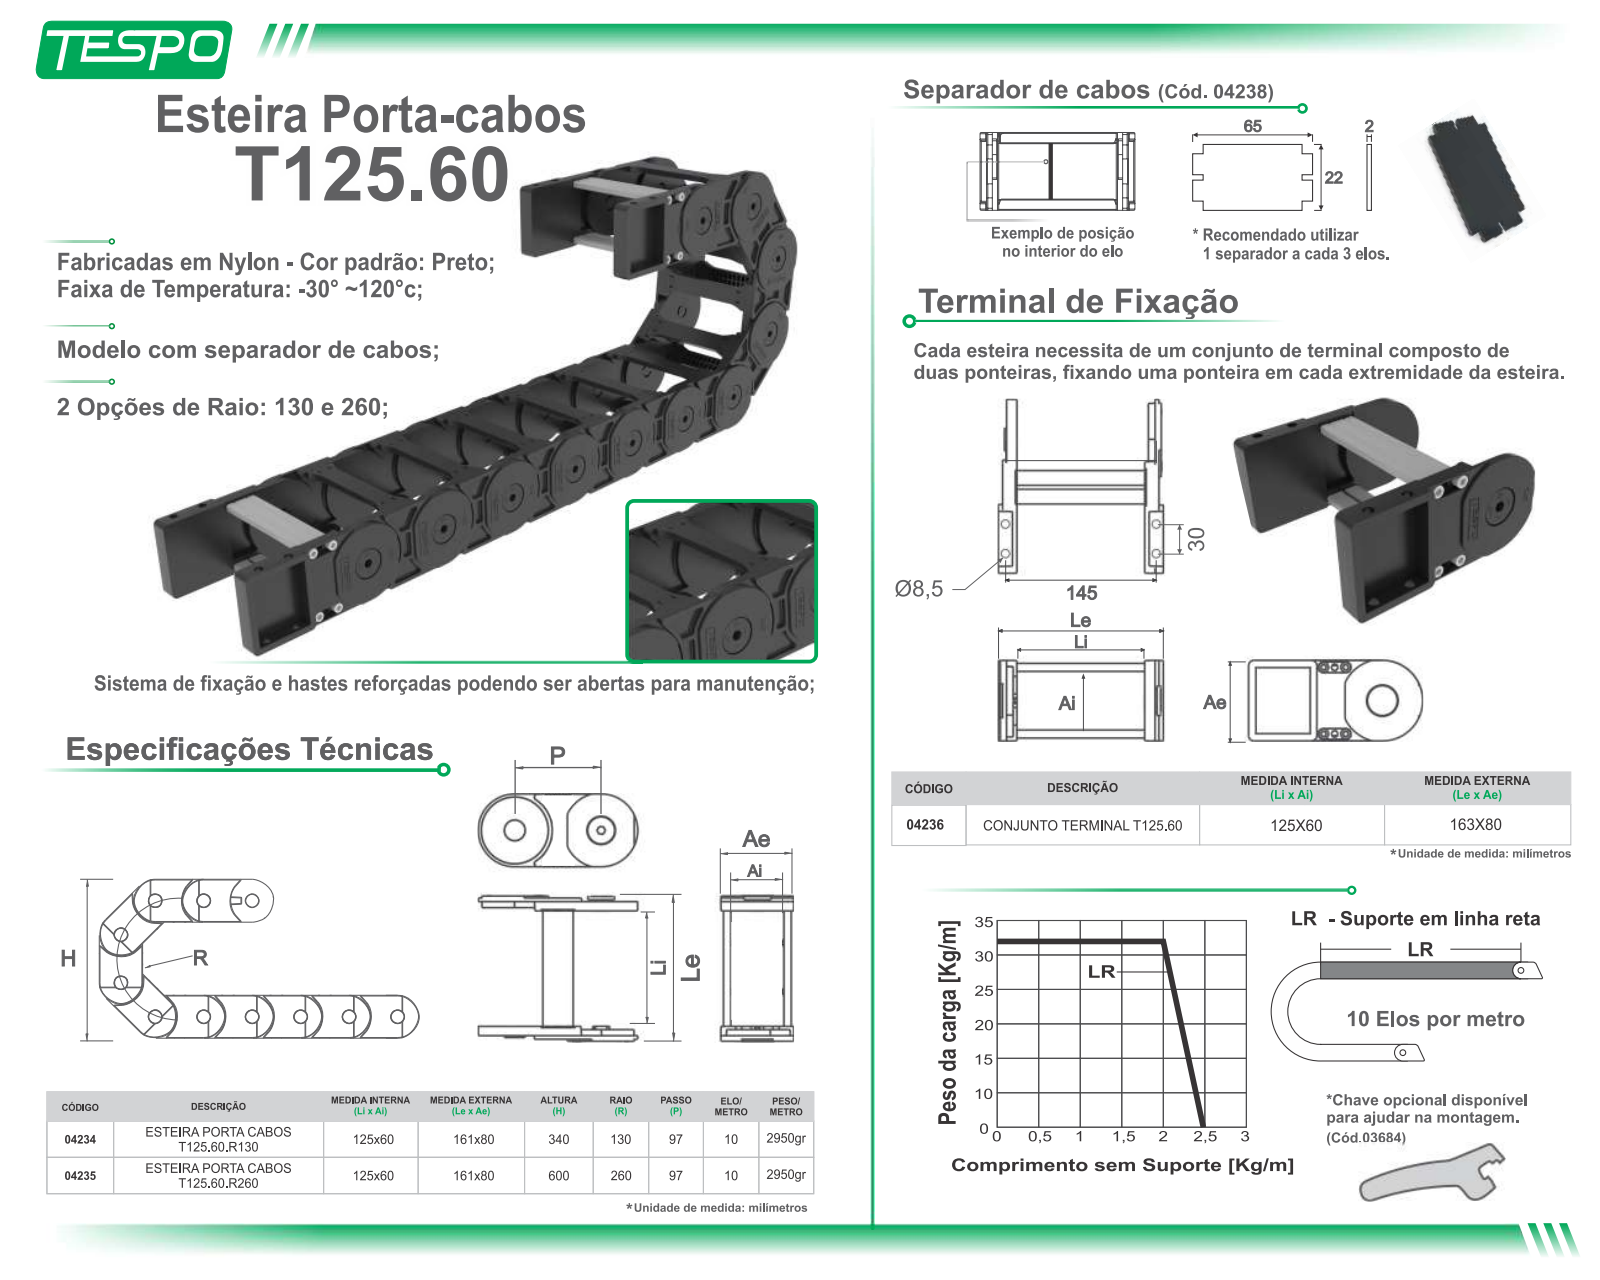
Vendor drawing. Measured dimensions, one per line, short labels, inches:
written by: ST-DEVELOPER v15 (AUTOMOTIVE_DESIGN)
unit: in
bodies: 1 solid, 74 faces (36 planar, 0 cylindrical, 38 other)
size: 7.047 × 6.244 × 3.228
volume: 18.92 in³; area: 143.4 in²
face distances: 0.661, 5.583, 0.322, 2.654, 0.524, 5.72, 0.138, 5.059, 0.516, 5.728
